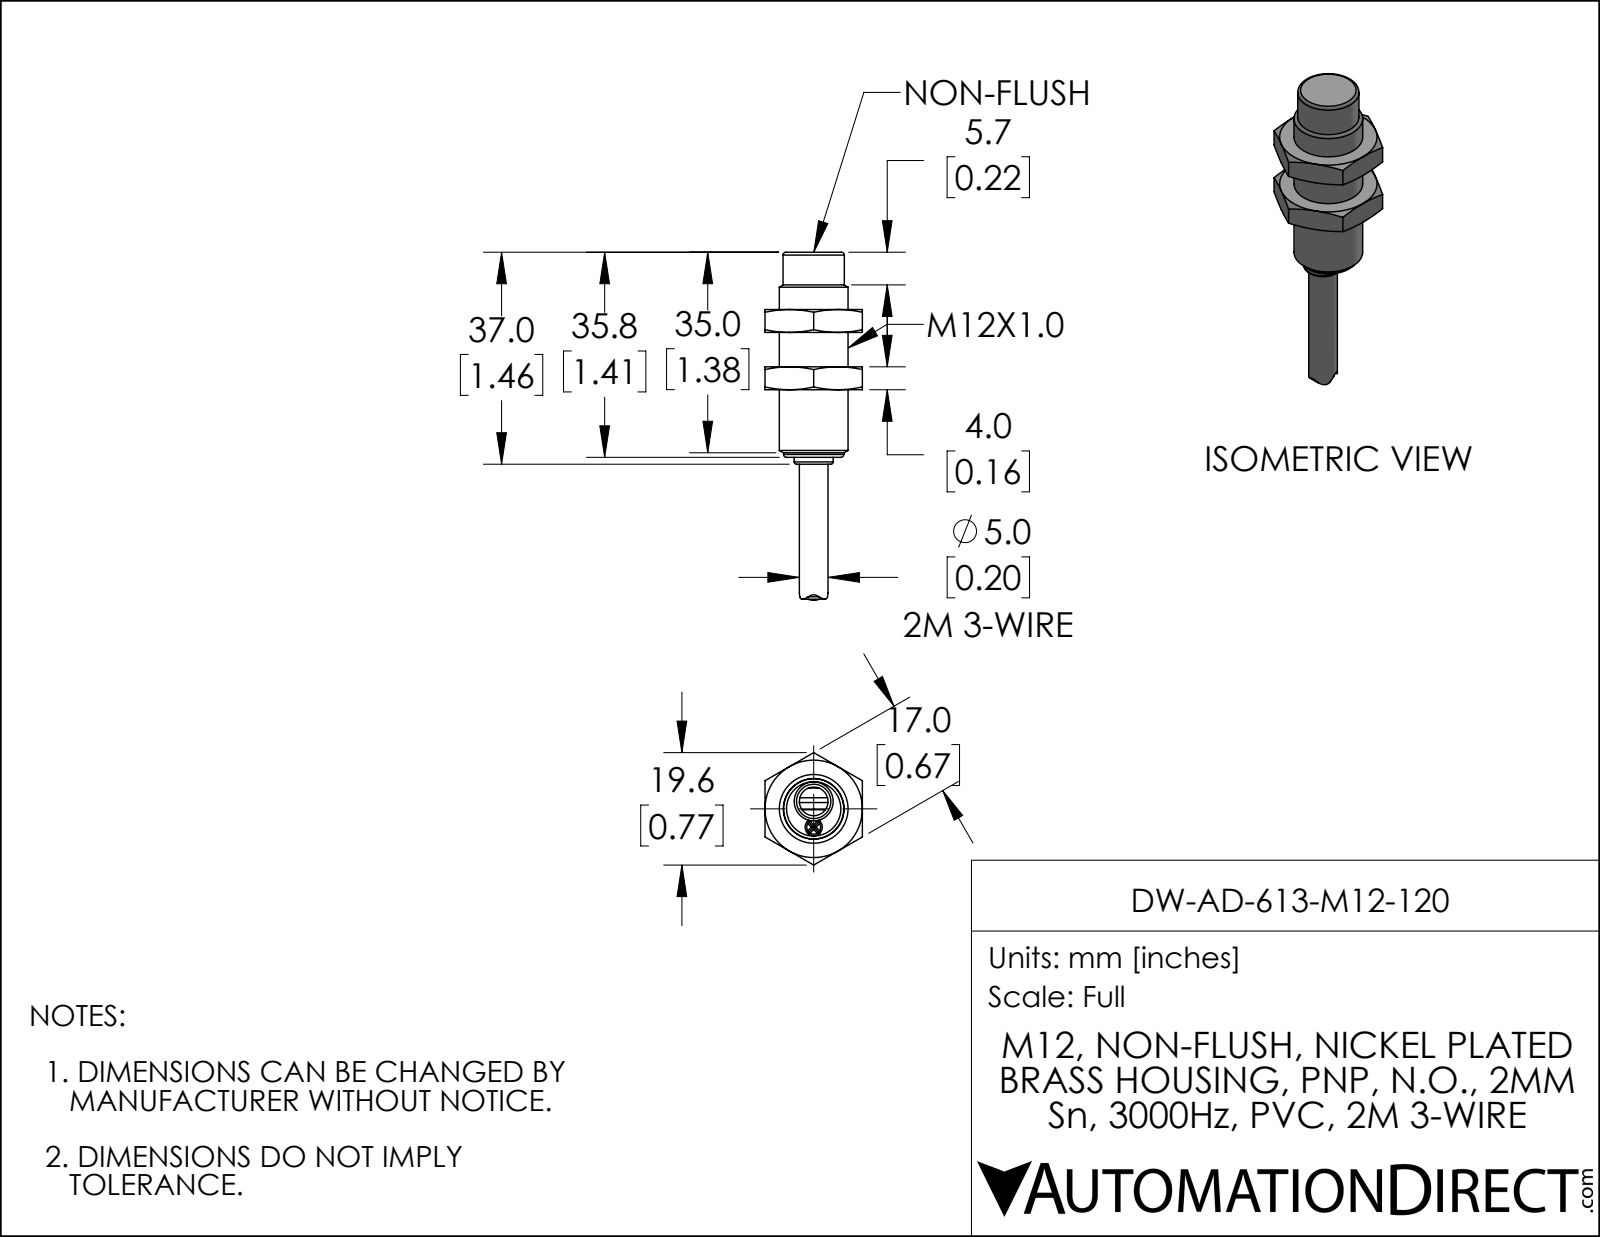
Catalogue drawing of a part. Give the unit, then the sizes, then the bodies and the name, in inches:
Units: inches
Overall size (bounding box): 2.392 × 0.773 × 0.669
Round bosses / shafts (diameter × count): ⌀0.472 ×1, ⌀0.421 ×1, ⌀0.413 ×1, ⌀0.268 ×1, ⌀0.197 ×1, ⌀0.118 ×1
Partial cylindrical surfaces — rounded edges, fillets, slot ends (radius × count): R0.031 ×1, R0.041 ×1, R0.165 ×1, R0.248 ×1, R0.331 ×1
Main face-to-face distances: 0.394, 0.157, 0.669, 0.551, 0.236, 0.787, 0.945, 1.409, 1.016, 0.858
Volume: 0.333 in³ · Surface area: 4.025 in²
Bodies: 1 solid, 80 faces (33 planar, 13 cylindrical, 34 other)
Part name (STEP PRODUCT): DW-AD-613-M12-120
STEP written by: SolidWorks 2019 (AUTOMOTIVE_DESIGN)
